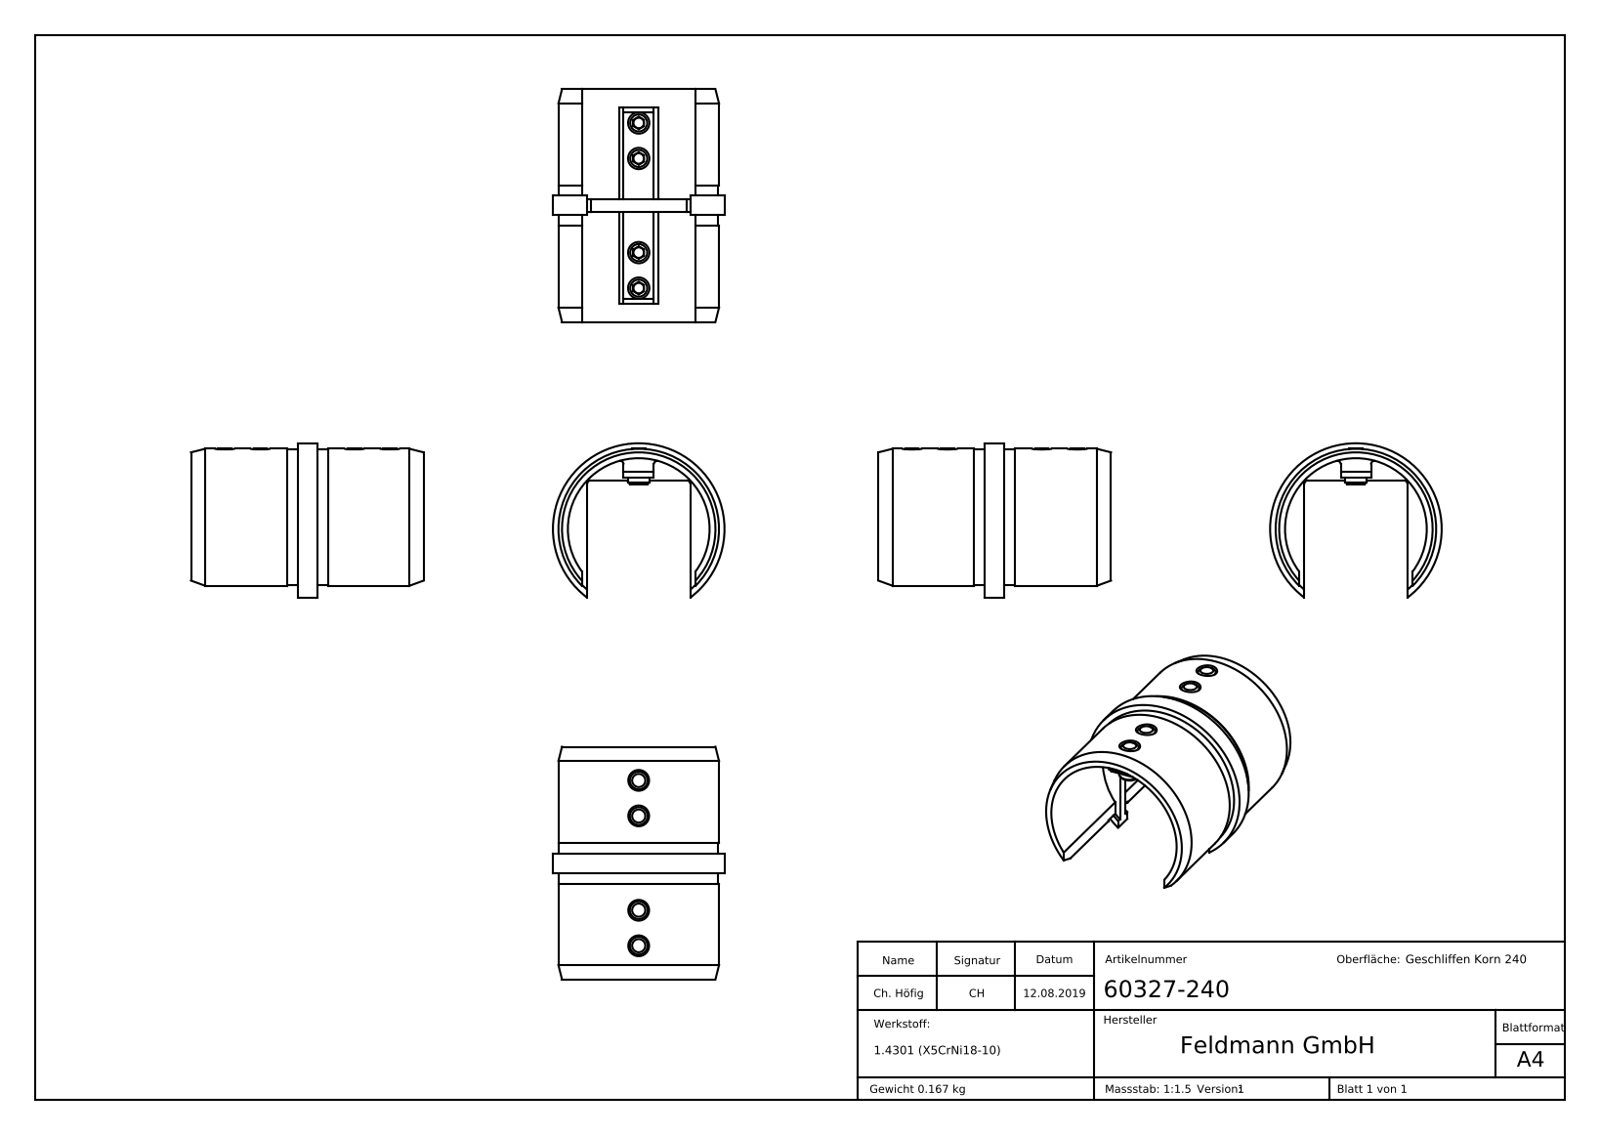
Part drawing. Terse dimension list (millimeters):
name: 6032X-240 Teil1_60327-240 Teil1; DIN913_DIN 913 M6x10; 60327-240
written by: SolidWorks 2015 (CONFIG_CONTROL_DESIGN)
unit: mm
bodies: 5 solids, 384 faces (200 planar, 45 cylindrical, 139 other)
size: 65.5 × 48.3 × 43.46
volume: 21 163 mm³; area: 16 568 mm²
holes: 4× ⌀5
bosses: 4× ⌀6, 1× ⌀48.3
rounds: 4× R1, 1× R19.95, 1× R22.4, 1× R22.6
face distances: 1.05, 4.45, 11.75, 20.25, 30, 31.05, 34.45, 35.5, 3.4, 30.5
hole spacings: 10, 36.5, 26.5, 46.5
